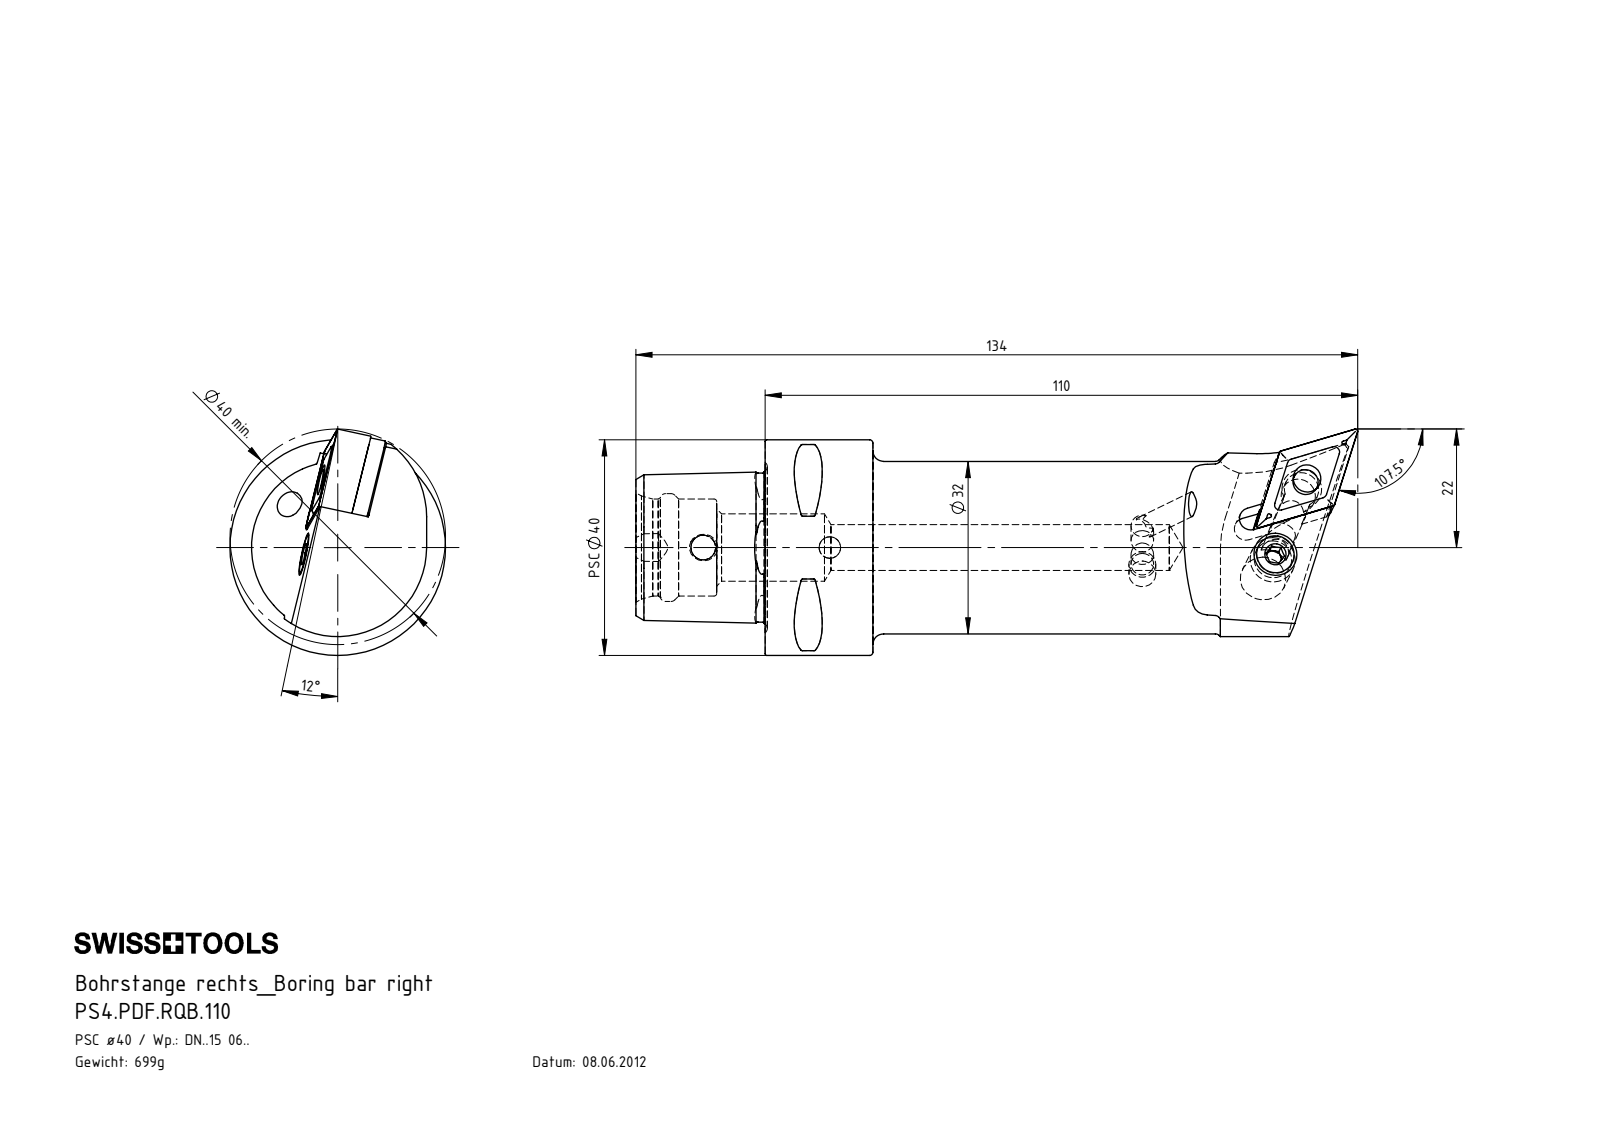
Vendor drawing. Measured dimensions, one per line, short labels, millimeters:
name: WCD-ER1.101.000; WCD-ER4.101.017_A; WDF-ER2.101.003_A; DNMG150604 (+4 more)
written by: SolidWorks 2017 (AUTOMOTIVE_DESIGN)
unit: mm
bodies: 8 solids, 358 faces (92 planar, 85 cylindrical, 181 other)
size: 134 × 42 × 40
volume: 89 857 mm³; area: 22 747 mm²
holes: 2× ⌀4, 1× ⌀4.2, 1× ⌀4.6, 1× ⌀5, 1× ⌀5.16, 1× ⌀6, 1× ⌀6.4, 1× ⌀7, 1× ⌀8.4, 1× ⌀8.5, 1× ⌀12.5, 1× ⌀18
bosses: 1× ⌀40, 1× ⌀32, 1× ⌀8, 1× ⌀7.9, 1× ⌀6.4, 1× ⌀4.7, 1× ⌀3.55
rounds: 8× R0.3, 4× R0.4, 4× R1, 2× R2.5, 2× R3, 1× R2.1, 1× R2.35, 1× R2.8
face distances: 6.05, 3.18, 9.23, 0.42, 12.7, 20, 24, 44, 15.52, 12.28
hole spacings: 15.58, 23.5
